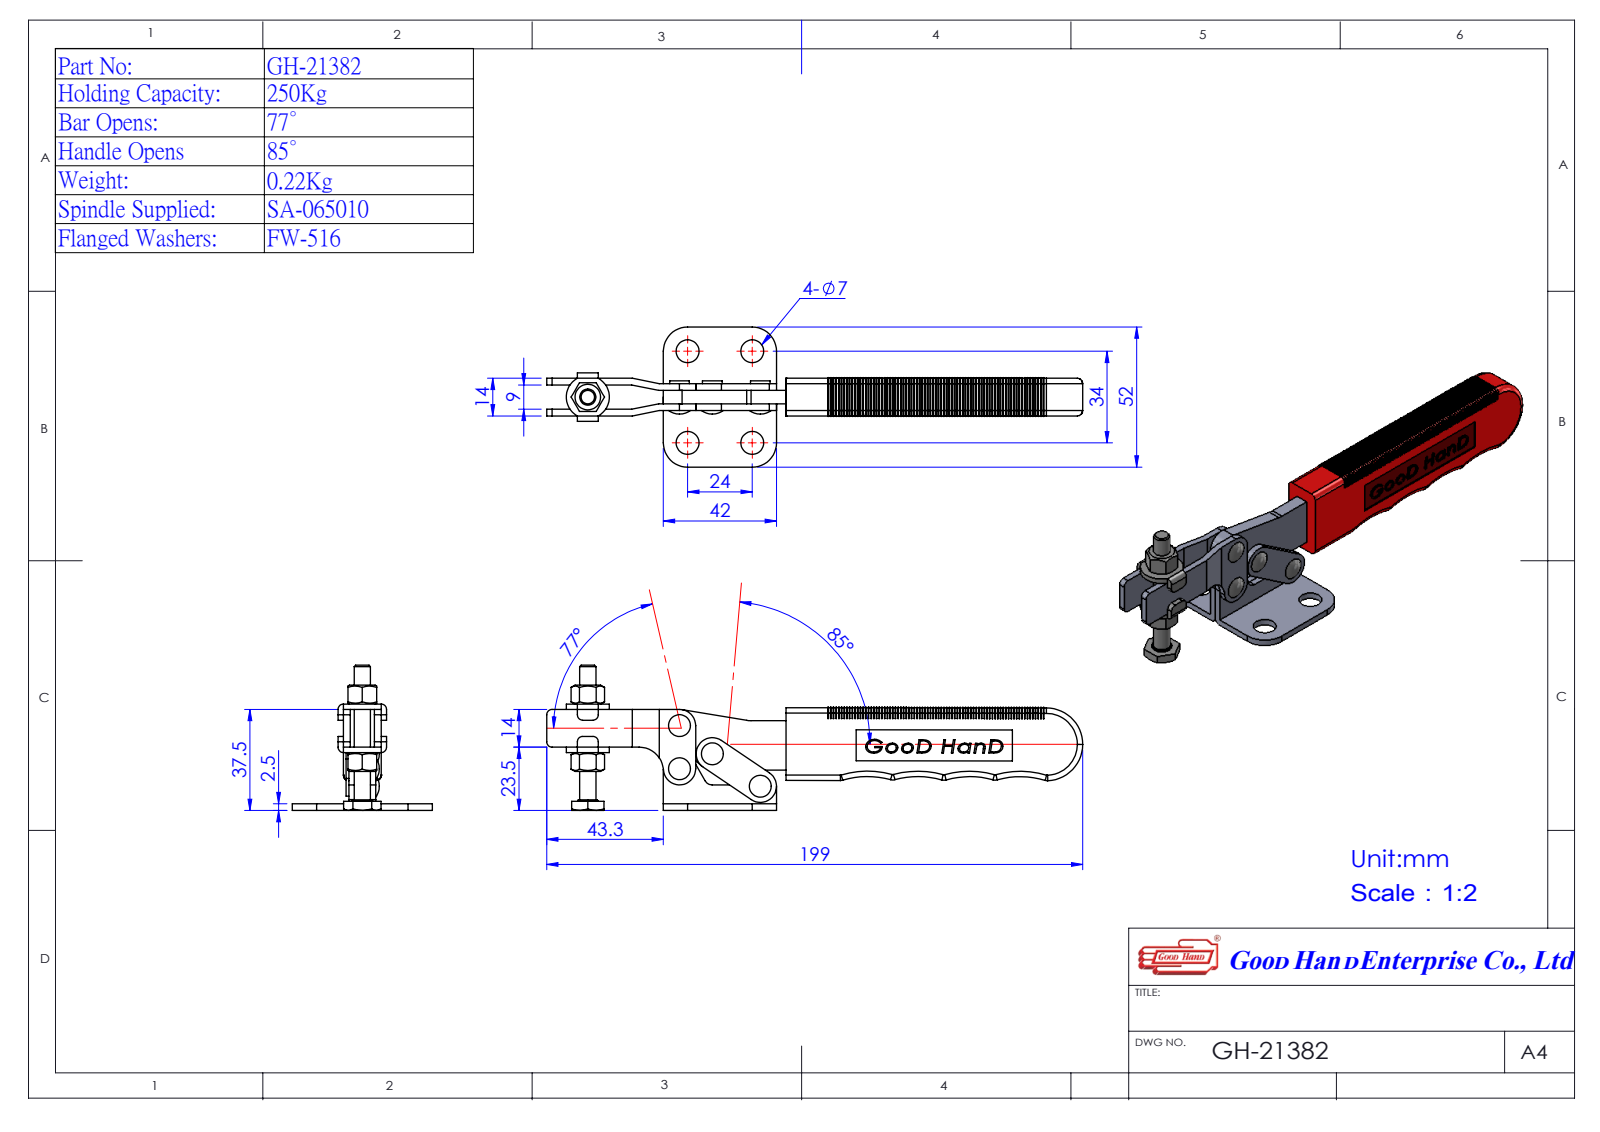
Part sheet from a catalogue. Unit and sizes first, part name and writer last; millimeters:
Units: millimetres
Overall size (bounding box): 198.99 × 53.9 × 52
Round holes (diameter × count): ⌀5 ×5, ⌀8.5 ×4
Round bosses / shafts (diameter × count): ⌀7.3 ×4, ⌀12 ×1, ⌀7.5 ×1, ⌀6 ×1
Partial cylindrical surfaces — rounded edges, fillets, slot ends (radius × count): R3 ×11, R2 ×10, R1 ×4, R32 ×4, R6 ×3, R8 ×1, R9 ×1, R10 ×1
Main face-to-face distances: 9.5, 2.5, 4.5, 14, 2, 5, 12, 7.5, 7, 11.5
Hole centre spacings: 24, 34, 41.62, 13.38, 16, 16.06, 21.5, 30.7
Volume: 61 332 mm³ · Surface area: 26 880 mm²
Bodies: 5 solids, 241 faces (111 planar, 108 cylindrical, 22 other)
Part name (STEP PRODUCT): Group3^GH-21382(簡化); Group2^GH-21382(簡化); Group5^GH-21382(簡化); Group4^GH-21382(簡化) (+2 more)
STEP written by: SolidWorks 2016 (AUTOMOTIVE_DESIGN)
